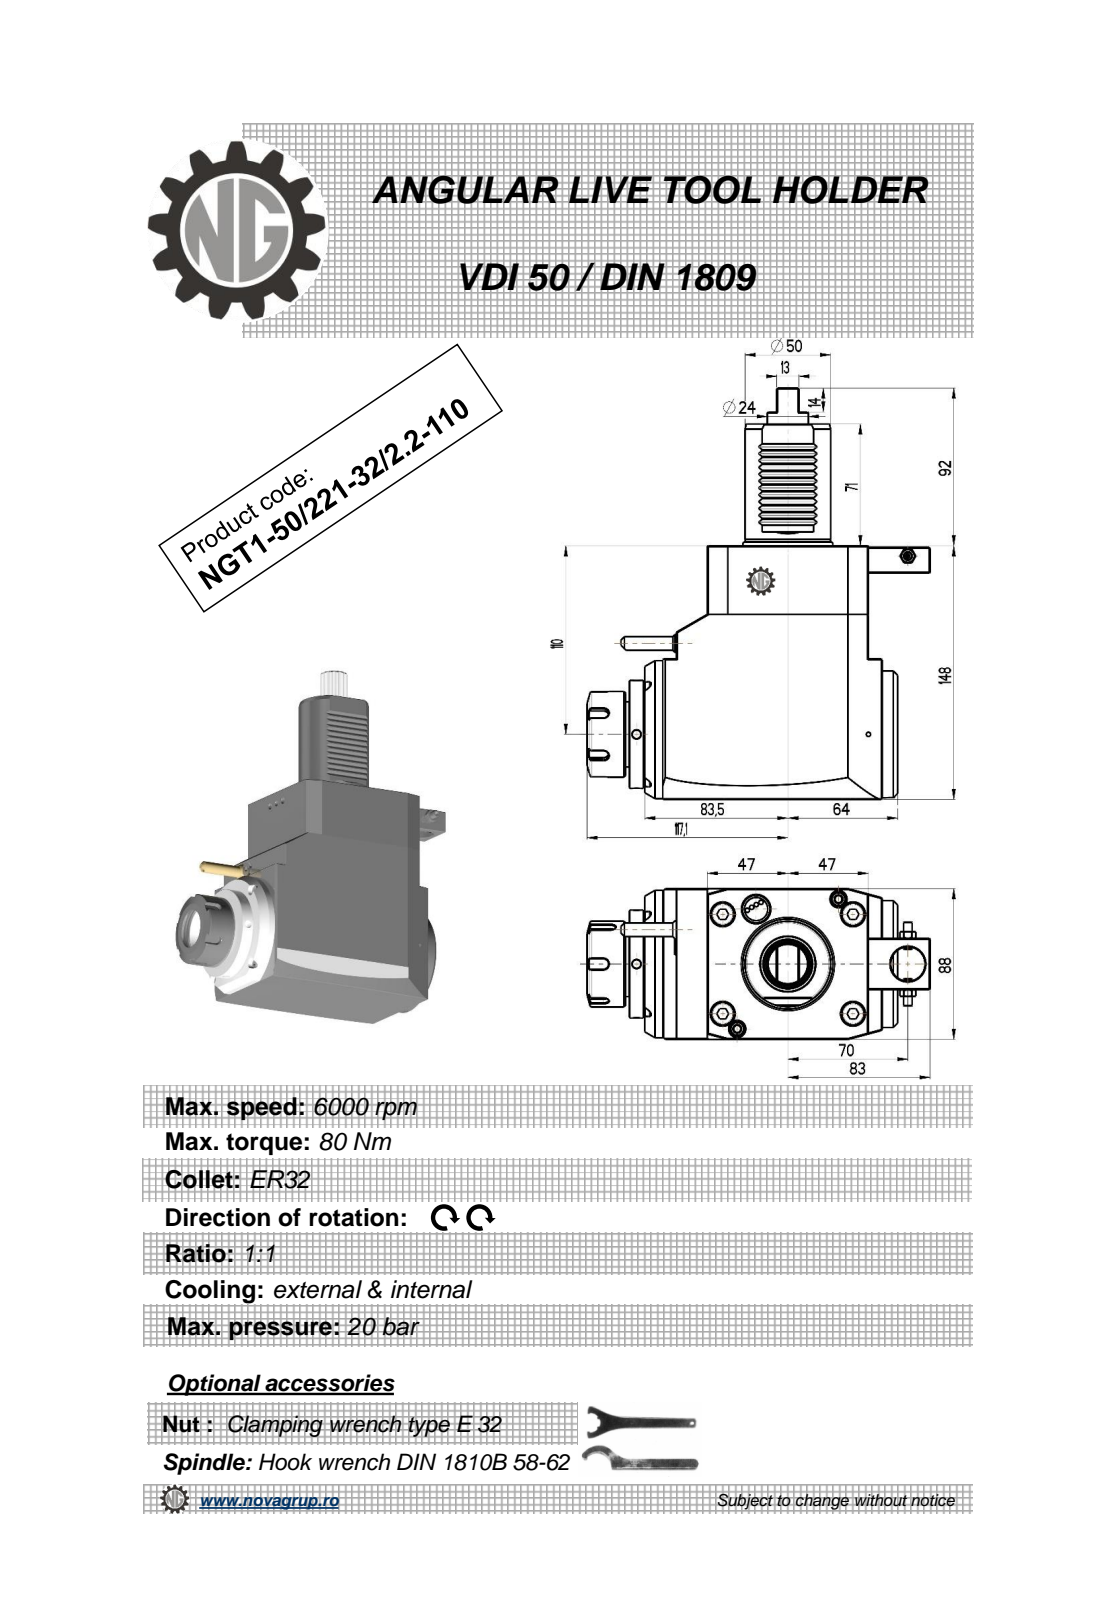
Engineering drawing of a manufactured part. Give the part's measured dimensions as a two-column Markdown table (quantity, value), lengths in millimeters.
| quantity | value |
| --- | --- |
| part name | NGT1_50_221_32_1_2_110 |
| STEP written by | PRO/ENGINEER BY PARAMETRIC TECHNOLOGY CORPORATION, 2010280 (CONFIG_CONTROL_DESIGN) |
| units | millimeters |
| bodies | 1 solid, 404 faces (195 planar, 91 cylindrical, 118 other) |
| overall size | 240 × 200.1 × 88 |
| volume | 1 801 000 mm³ |
| surface area | 112 068 mm² |
| round holes (diameter × count) | 5 × 3, 3 × 1, 4.5 × 1, 9.5 × 1, 20 × 1, 27 × 1 |
| round bosses / shafts (diameter × count) | 50 × 2, 86 × 1, 74 × 1, 63 × 1, 50.5 × 1, 41 × 1, 24 × 1, 10 × 1 |
| partial cylindrical surfaces (radius × count) | 0.26 × 12, 0.3 × 12, 0.2 × 6, 3 × 5, 0.8 × 2, 2.5 × 1 |
| main face-to-face distances | 88, 148, 147.5, 9, 17, 8, 94, 111, 36.5, 130.5 |
| hole center spacings | 52.46, 56.65, 101.5, 158.25 |
